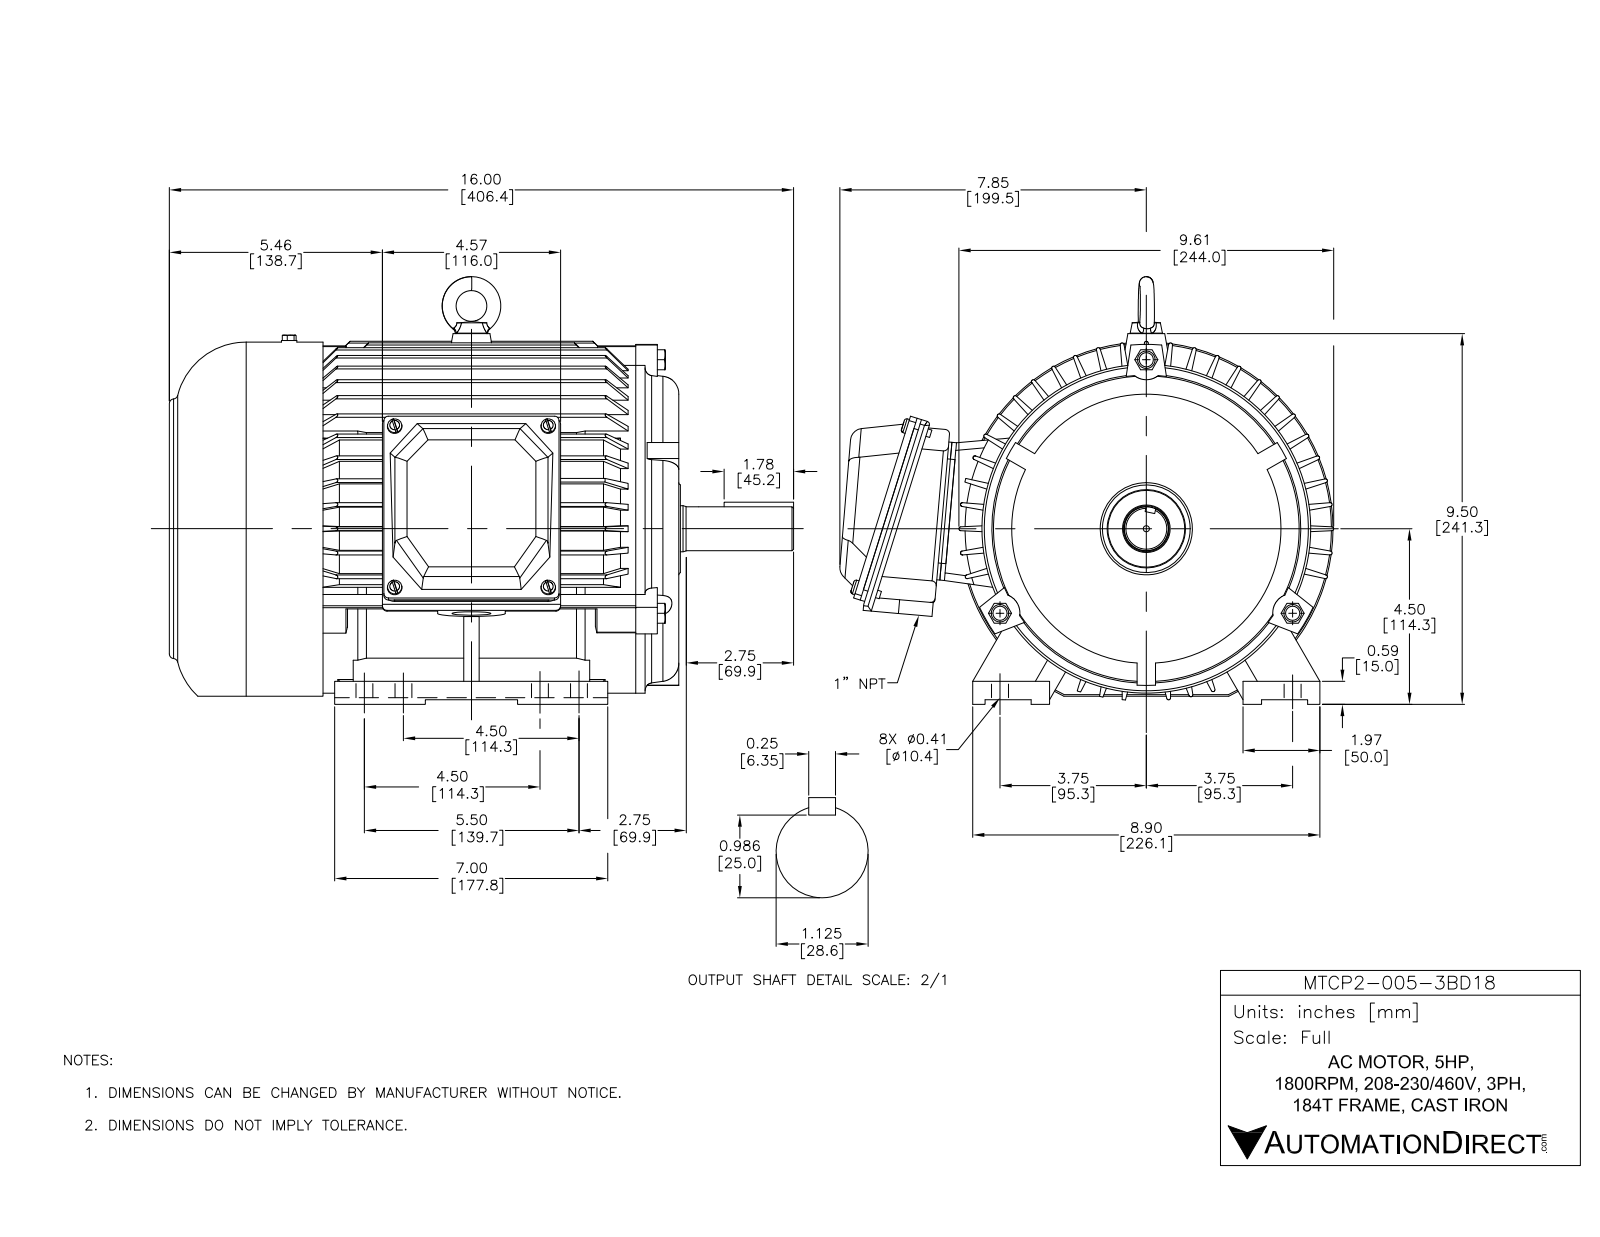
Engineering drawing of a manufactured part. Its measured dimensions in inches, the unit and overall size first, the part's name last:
Units: inches
Overall size (bounding box): 15.999 × 12.659 × 10.961
Round holes (diameter × count): ⌀0.228 ×8, ⌀0.433 ×8, ⌀0.276 ×6, ⌀0.197 ×4, ⌀0.236 ×4, ⌀0.362 ×3, ⌀0.394 ×3, ⌀0.315 ×1, ⌀1 ×1, ⌀1.181 ×1, ⌀1.969 ×1, ⌀2.047 ×1
Round bosses / shafts (diameter × count): ⌀0.315 ×4, ⌀0.197 ×4, ⌀0.283 ×3, ⌀9.567 ×1, ⌀1.496 ×1, ⌀1.126 ×1, ⌀0.394 ×1
Partial cylindrical surfaces — rounded edges, fillets, slot ends (radius × count): R0.02 ×256, R0.118 ×14, R0.049 ×13, R0.059 ×8, R0.157 ×8, R0.276 ×8, R0.315 ×8, R0.091 ×6
Main face-to-face distances: 8.425, 0.039, 1.102, 9.528, 0.236, 0.118, 0.866, 9.291, 12.959, 11.857
Hole centre spacings: 3.937, 2.677, 3.786, 4.331, 5.853, 1, 2.678, 4.33
Volume: 567.4 in³ · Surface area: 1 427 in²
Bodies: 15 solids, 1637 faces (744 planar, 580 cylindrical, 313 other)
Part name (STEP PRODUCT): PEWWE-184T
STEP written by: SolidWorks 2017 (AUTOMOTIVE_DESIGN)
